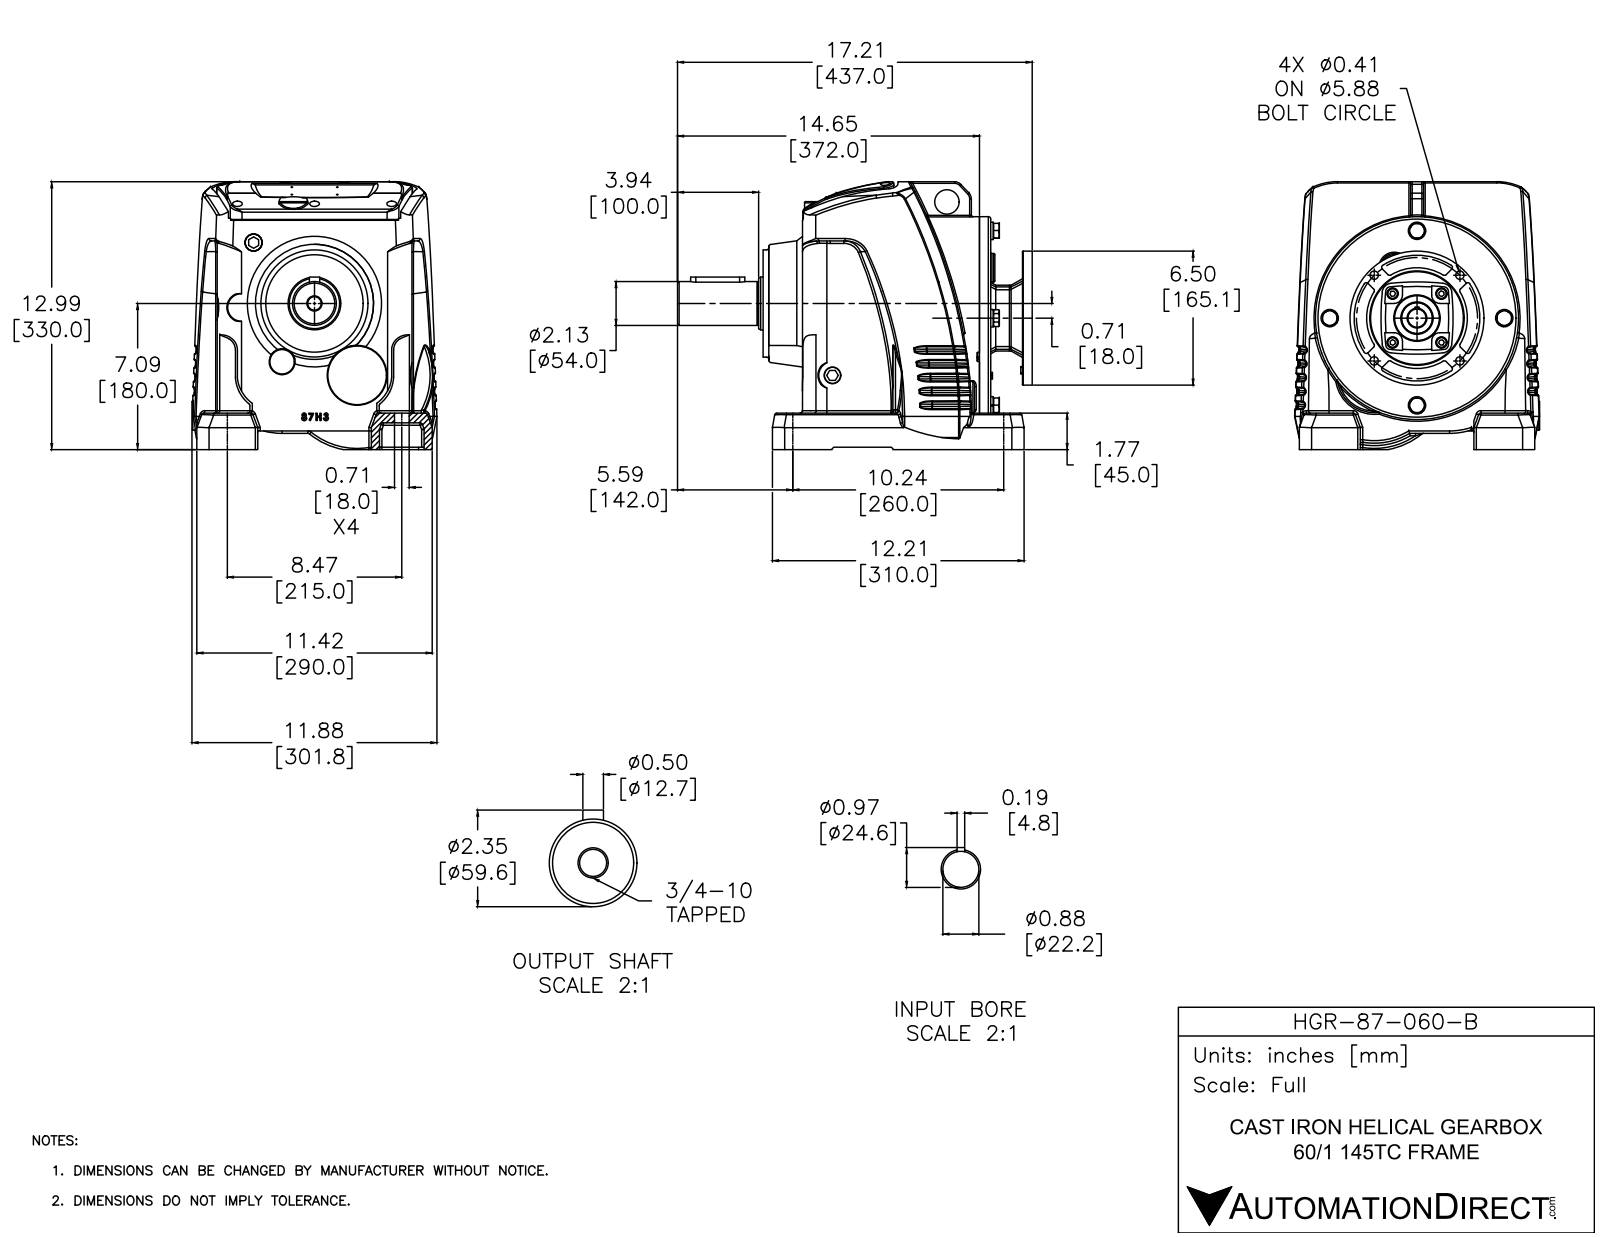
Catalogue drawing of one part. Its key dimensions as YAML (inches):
part_name: "HGR-87-060-B"
step_written_by: "SolidWorks 2015 (CONFIG_CONTROL_DESIGN)"
units: inches
bodies: {solids: 8, faces: 1311, planar: 304, cylindrical: 306, other: 701}
overall_size: [17.205, 12.992, 11.882]
volume: 1078
surface_area: 1187
round_holes:
  - {diameter: 0.472, count: 7}
  - {diameter: 0.079, count: 4}
  - {diameter: 0.406, count: 4}
  - {diameter: 0.551, count: 4}
  - {diameter: 0.709, count: 4}
  - {diameter: 0.839, count: 3}
  - {diameter: 0.656, count: 1}
  - {diameter: 0.875, count: 1}
  - {diameter: 0.878, count: 1}
  - {diameter: 1.181, count: 1}
  - {diameter: 1.378, count: 1}
  - {diameter: 1.575, count: 1}
round_bosses_or_shafts:
  - {diameter: 0.846, count: 4}
  - {diameter: 0.512, count: 4}
  - {diameter: 9.843, count: 1}
  - {diameter: 6.5, count: 1}
  - {diameter: 5.494, count: 1}
  - {diameter: 5.197, count: 1}
  - {diameter: 4.724, count: 1}
  - {diameter: 2.835, count: 1}
partial_cylinders:
  - {radius: 0.118, count: 76}
  - {radius: 0.079, count: 12}
  - {radius: 0.591, count: 10}
  - {radius: 0.394, count: 8}
  - {radius: 0.157, count: 4}
  - {radius: 0.709, count: 4}
  - {radius: 11.811, count: 4}
  - {radius: 0.039, count: 3}
face_to_face_distances: [0.039, 0.394, 8.465, 2.559, 0.591, 9.6, 9.134, 9.64, 1.575, 7.874]
hole_center_spacings: [1.673, 2.937, 3.381, 4.154, 2.874, 1.207, 1.264, 1.265]
